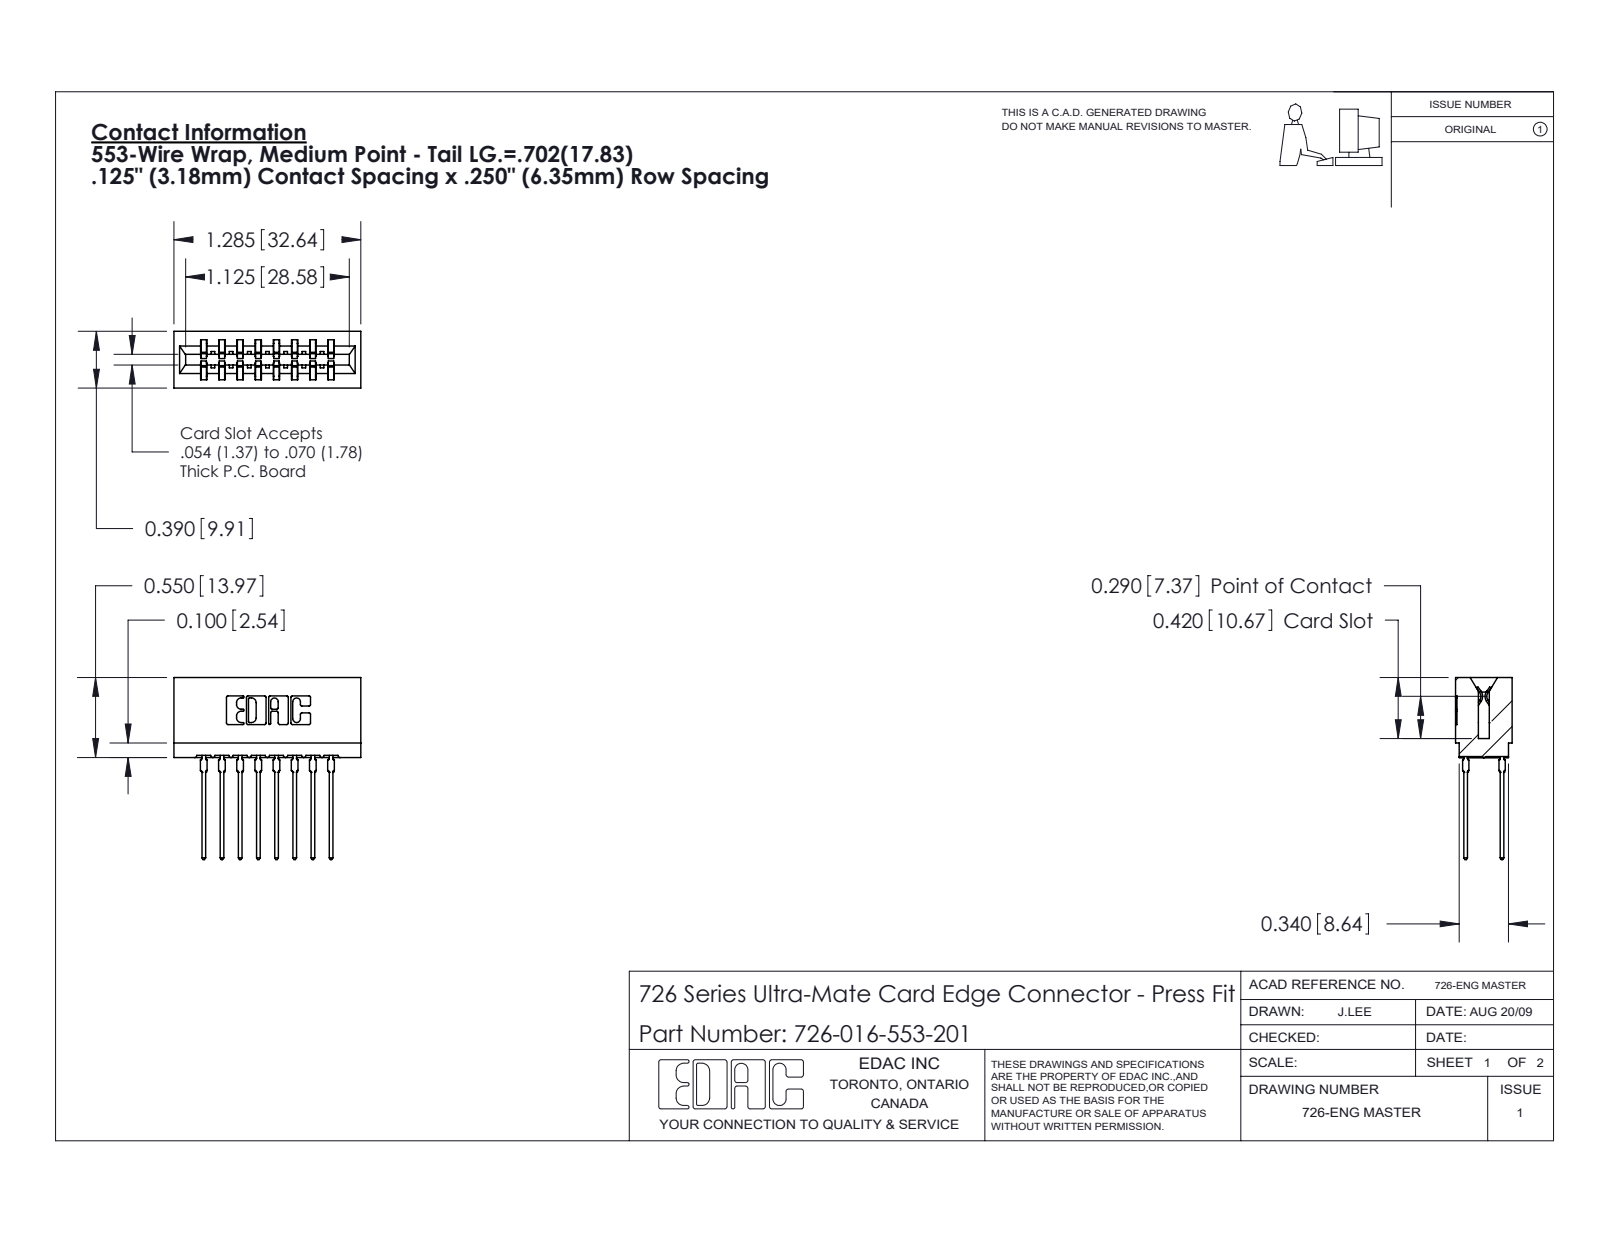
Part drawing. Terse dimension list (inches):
name: 726-016-553-201; 746-292-001_553; 726 Part_.515 Slot Depth - 01
written by: SolidWorks 2020 (CONFIG_CONTROL_DESIGN)
unit: in
bodies: 17 solids, 1529 faces (791 planar, 322 cylindrical, 416 other)
size: 1.285 × 1.251 × 0.39
volume: 0.199 in³; area: 7.975 in²
rounds: 32× R0.021, 22× R0.01, 9× R0.015, 8× R0.005, 8× R0.011, 6× R0.007, 6× R0.031, 3× R0.026
face distances: 0.25, 0.057, 0.333, 0.042, 0.125, 0.5, 0.083, 0.025, 0.307, 0.208
